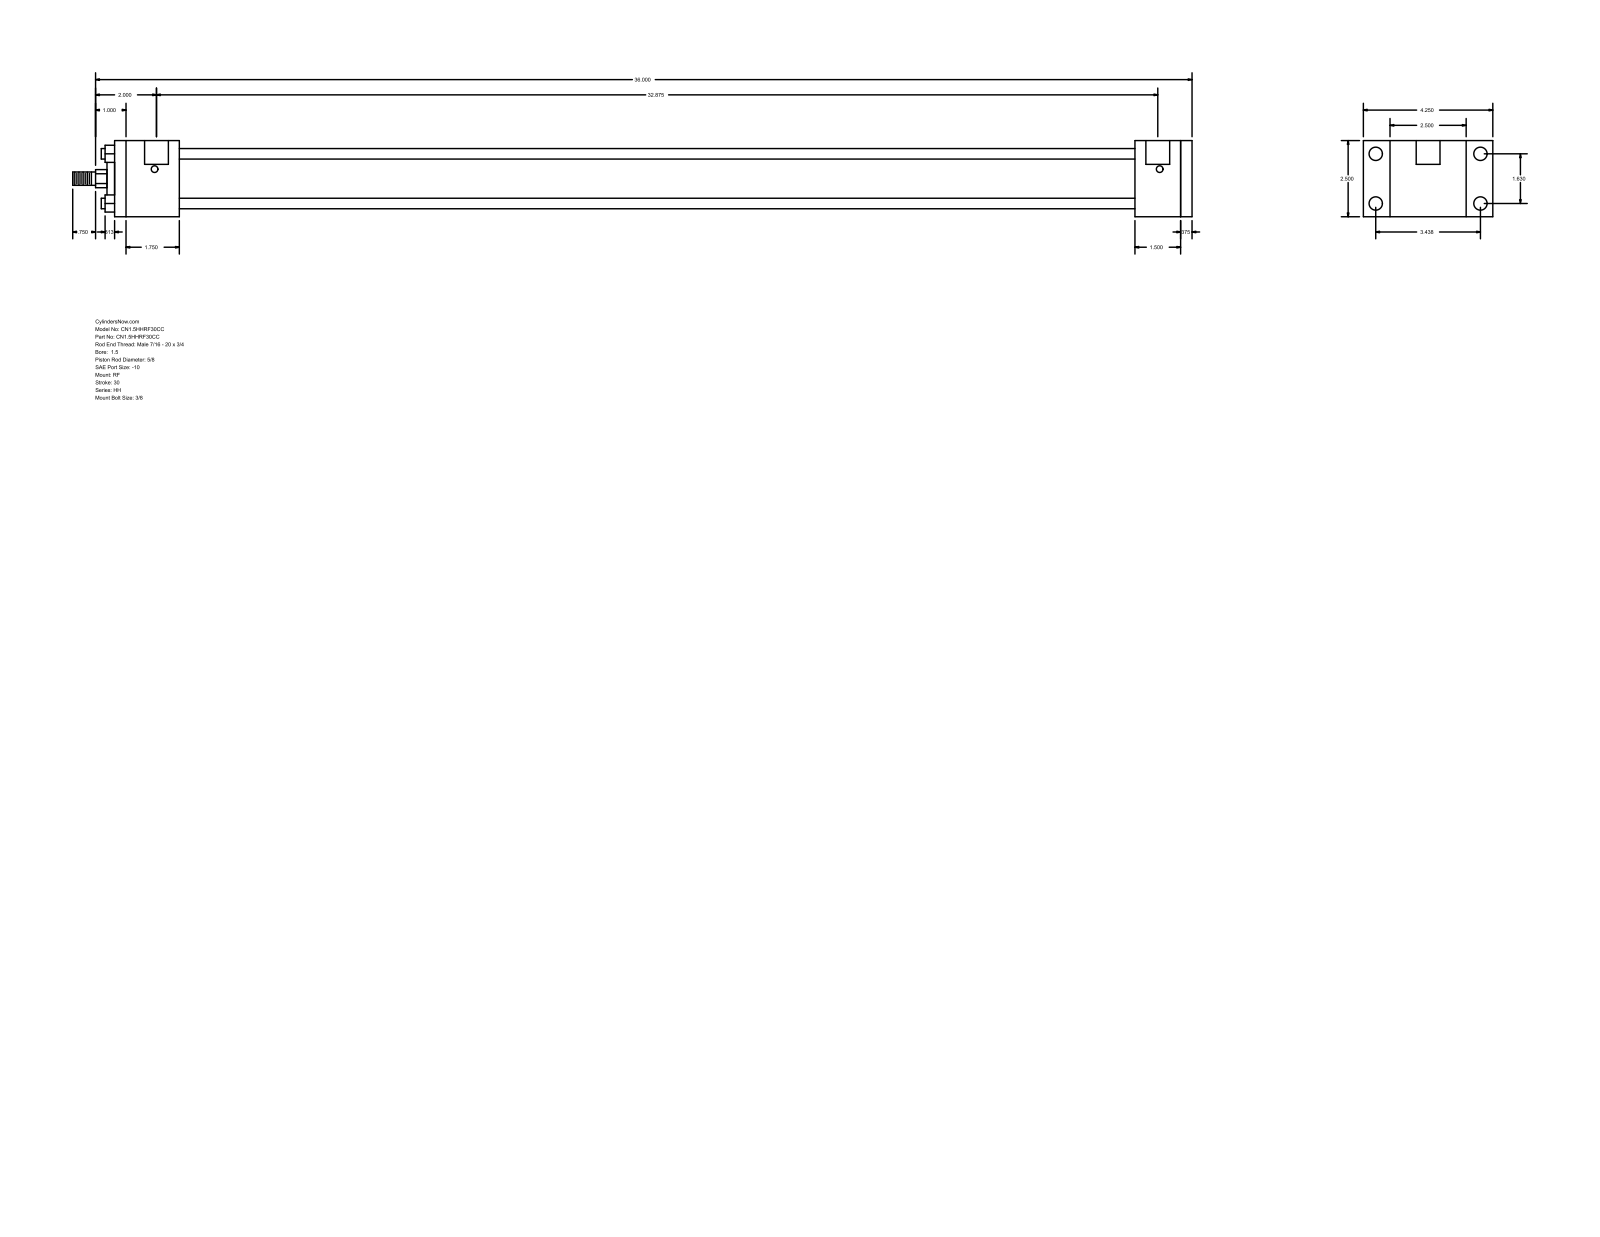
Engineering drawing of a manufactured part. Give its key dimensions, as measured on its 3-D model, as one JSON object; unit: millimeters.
{"part_name": "HH_RF__0150_0.625", "step_written_by": "GSSL Pune (CONFIG_CONTROL_DESIGN)", "units": "millimeters", "bodies": {"solids": 0, "faces": 92, "planar": 64, "cylindrical": 28, "other": 0}, "overall_size": [933.45, 107.95, 63.5], "round_holes": [[5.56, 4], [11.13, 4], [19.84, 2]], "round_bosses_or_shafts": [[8.76, 4], [44.45, 1], [28.57, 1], [15.88, 1], [11.11, 1]], "partial_cylinders_radius": [[7.54, 1]], "face_to_face_distances": [63.5, 898.52, 889, 9.52, 47.63, 53.97, 850.89, 796.92, 835.03, 844.55], "hole_center_spacings": [41.4, 87.32, 96.64, 838.2, 1.58, 1.59, 835.03, 836.61]}
